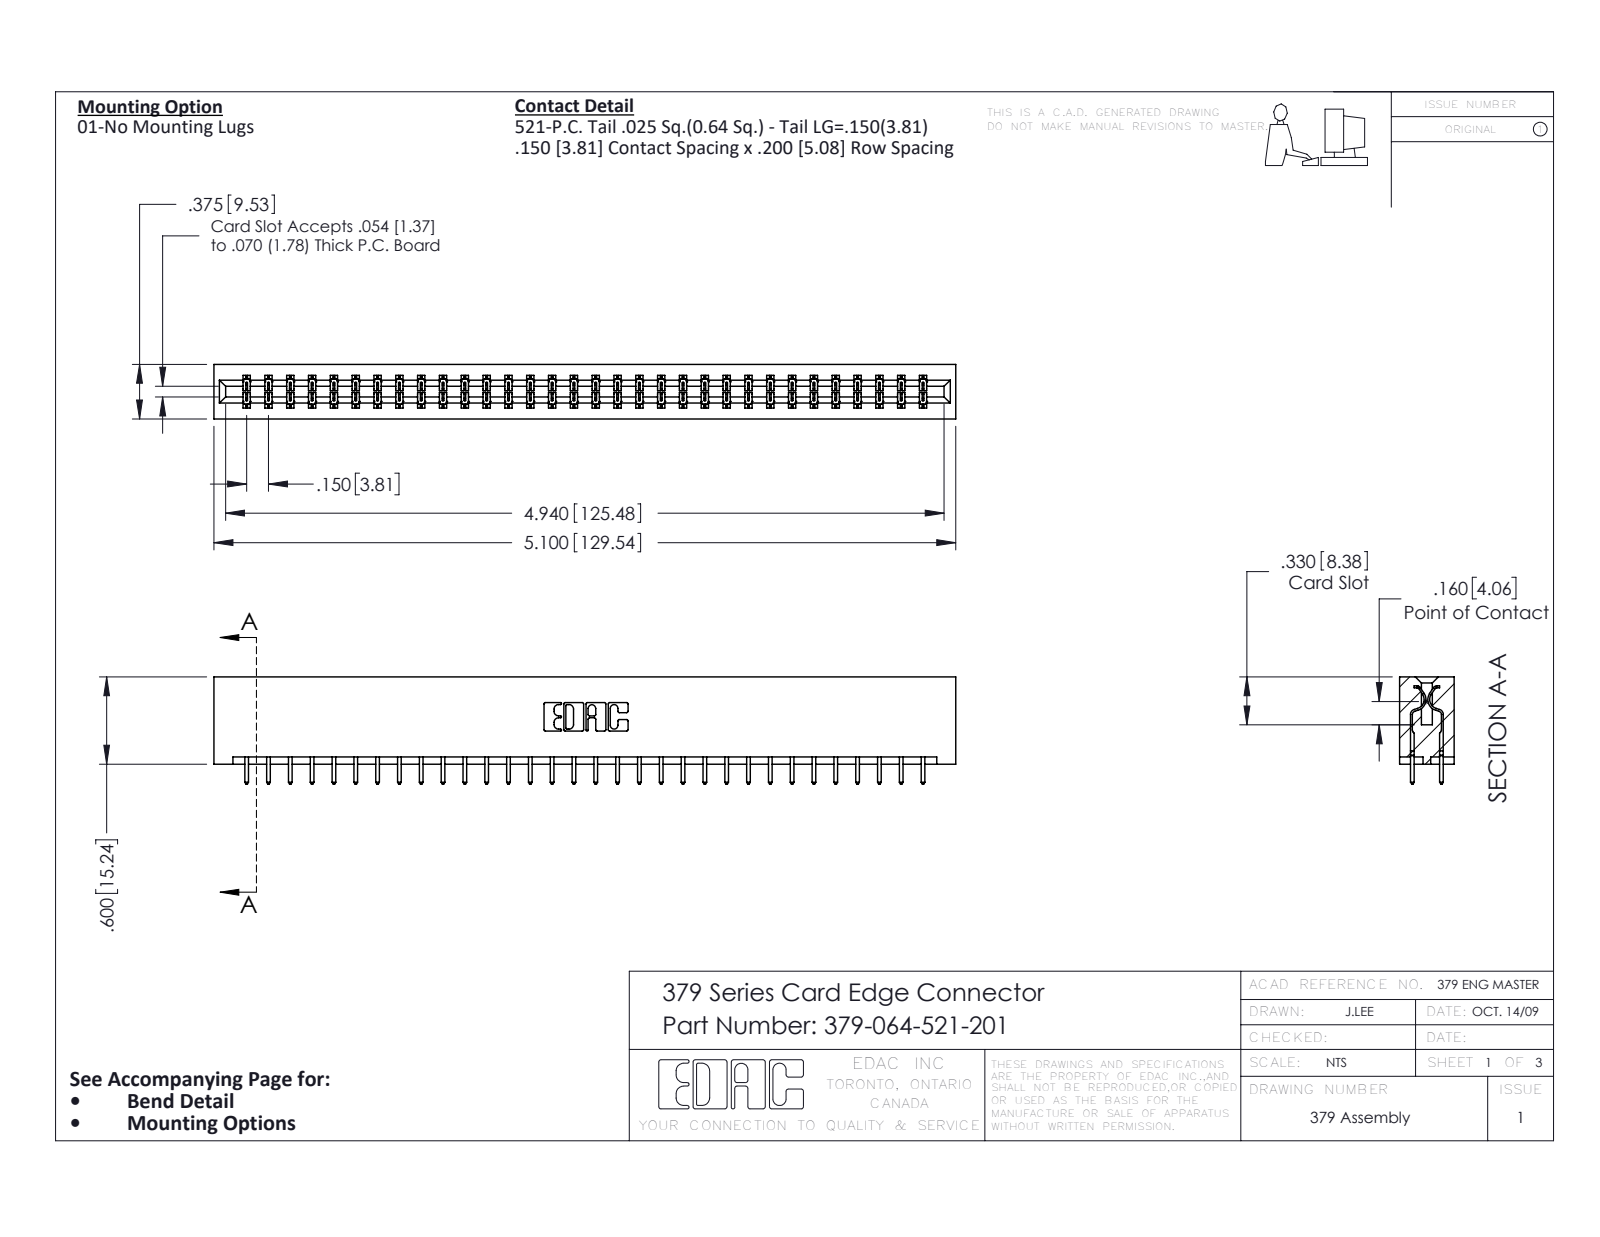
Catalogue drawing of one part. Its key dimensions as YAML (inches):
part_name: "345-292-001_345-293-121; 379 Part_Lugless; 379-064-521-201"
step_written_by: "SolidWorks 2016 (CONFIG_CONTROL_DESIGN)"
units: inches
bodies: {solids: 65, faces: 3434, planar: 2370, cylindrical: 1064, other: 0}
overall_size: [5.1, 0.737, 0.375]
volume: 0.878
surface_area: 24.69
partial_cylinders:
  - {radius: 0.006, count: 96}
  - {radius: 0.01, count: 64}
  - {radius: 0.01, count: 22}
  - {radius: 0.007, count: 6}
  - {radius: 0.031, count: 6}
  - {radius: 0.026, count: 3}
  - {radius: 0.014, count: 2}
  - {radius: 0.022, count: 2}
face_to_face_distances: [0.3, 0.075, 0.375, 0.2, 0.1, 0.225, 0.15, 0.076, 0.55, 0.275]
